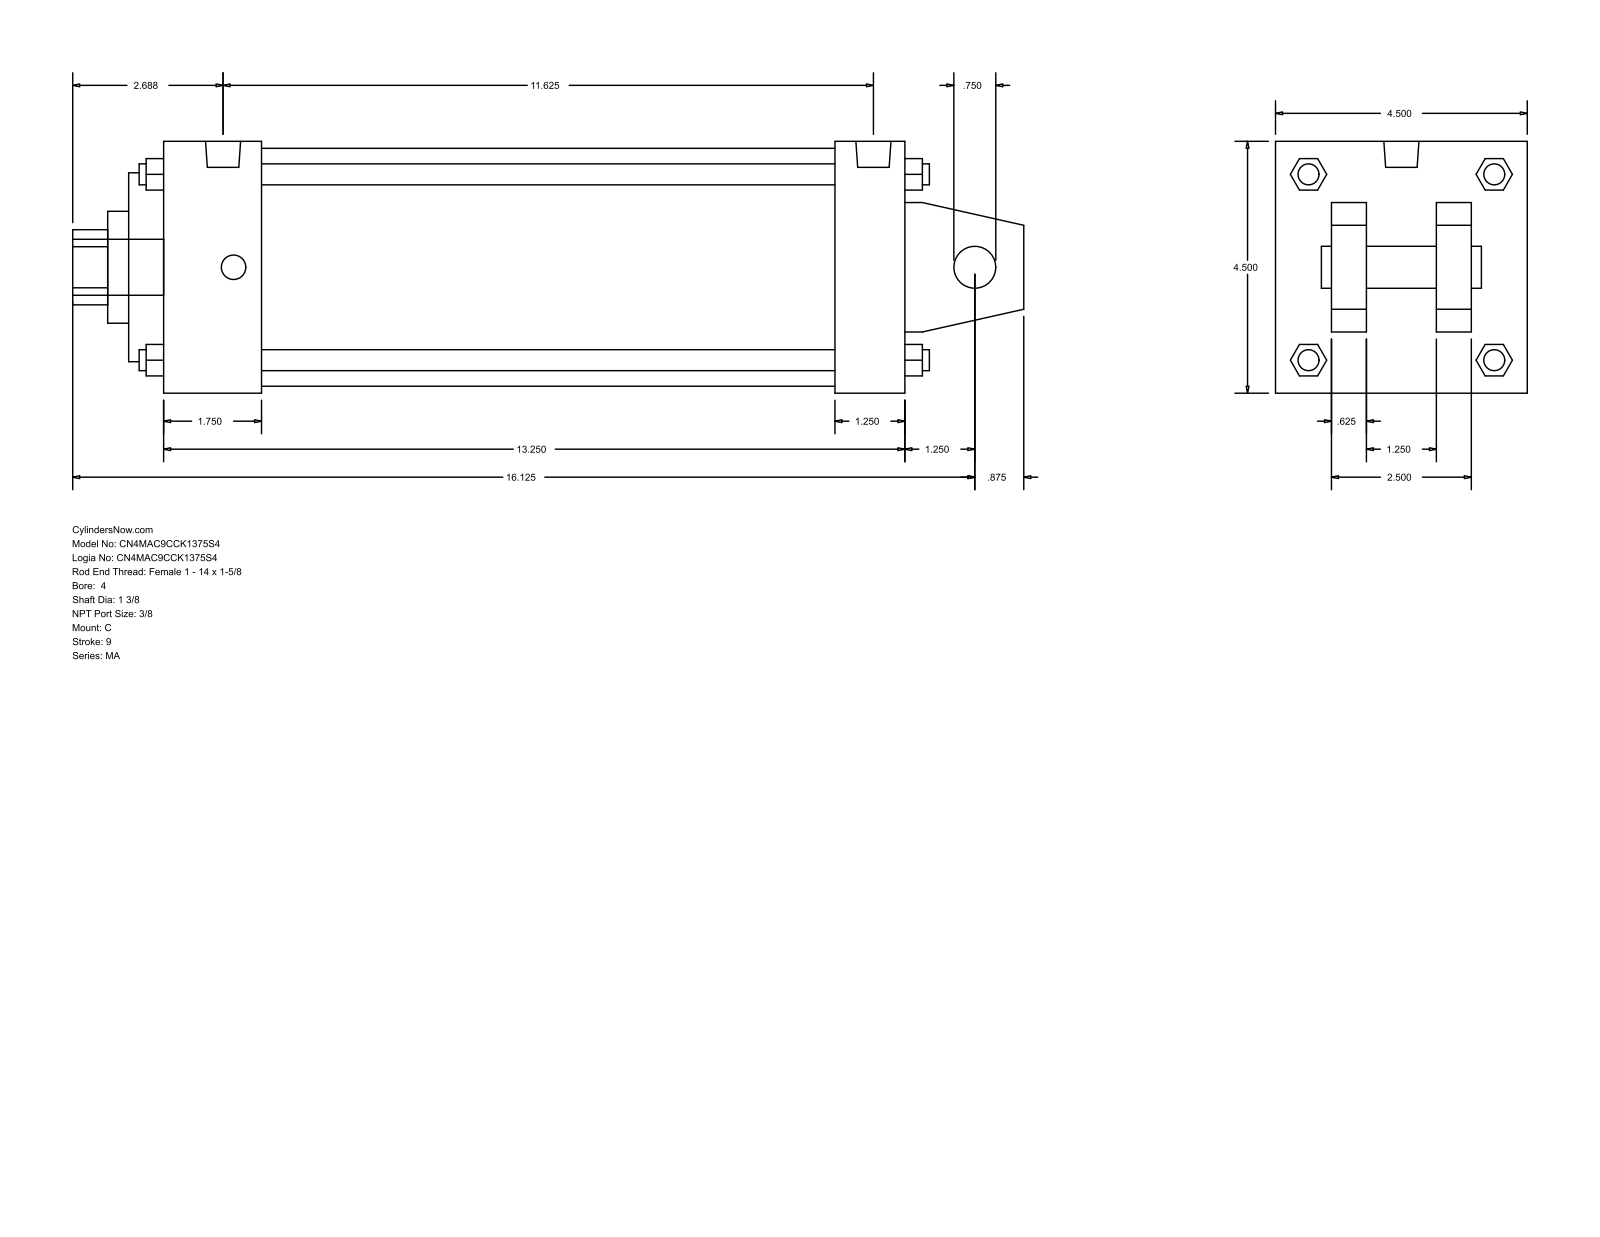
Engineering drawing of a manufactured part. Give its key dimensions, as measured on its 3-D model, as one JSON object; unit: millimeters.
{"part_name": "MA_C__0400_1.375", "step_written_by": "GSSL Pune (CONFIG_CONTROL_DESIGN)", "units": "millimeters", "bodies": {"solids": 0, "faces": 141, "planar": 109, "cylindrical": 32, "other": 0}, "overall_size": [431.8, 114.3, 114.3], "round_holes": [[19.05, 1], [34.92, 1], [50.8, 1], [85.72, 1], [107.95, 1]], "round_bosses_or_shafts": [[11.11, 4], [9.53, 4], [15.93, 2], [25.4, 1]], "partial_cylinders_radius": [[17.06, 1]], "face_to_face_distances": [114.3, 15.87, 336.55, 73.03, 41.27, 25.4, 88.9, 47.63, 352.42, 320.67]}
